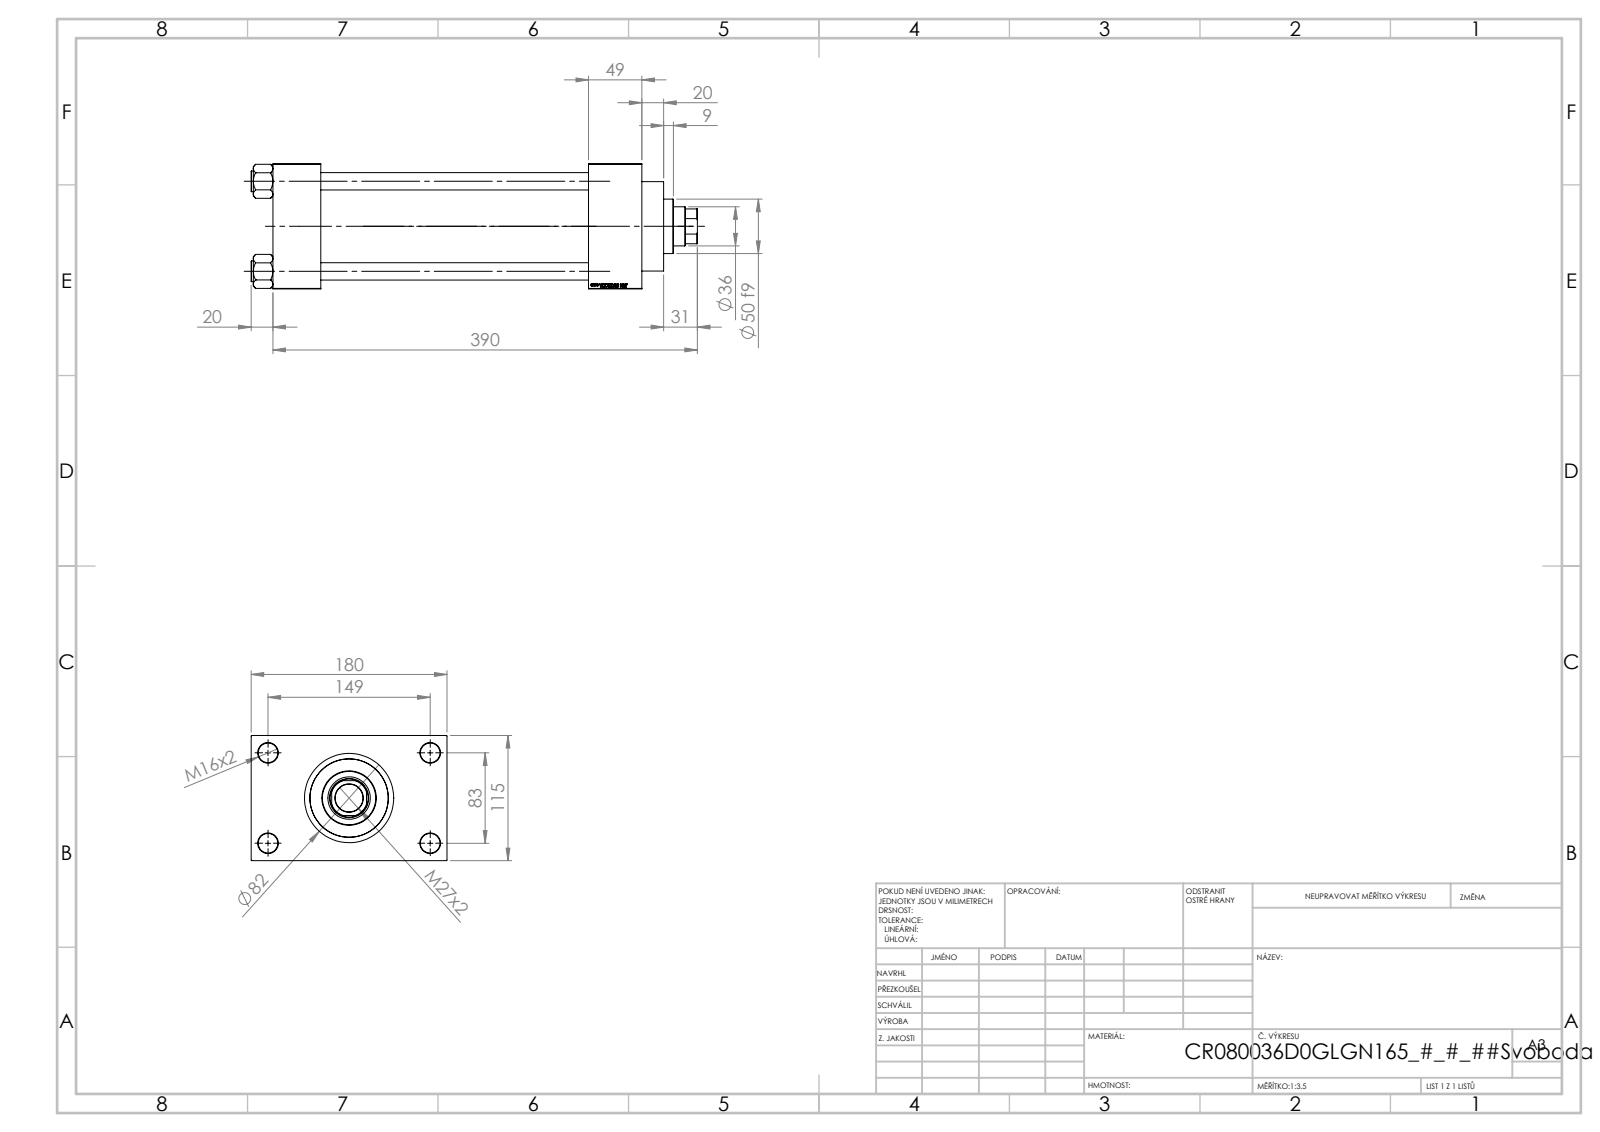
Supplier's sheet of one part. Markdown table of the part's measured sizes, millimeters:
| quantity | value |
| --- | --- |
| part name | V215CR_VCP_D; V215CR_D_Body; V215CR_D_TYCINKA; NUT_M5_D (+1 more) |
| STEP written by | SolidWorks 2019 (CONFIG_CONTROL_DESIGN) |
| units | millimeters |
| bodies | 11 solids, 1152 faces (545 planar, 89 cylindrical, 518 other) |
| overall size | 410 × 180 × 115 |
| volume | 2 466 000 mm³ |
| surface area | 444 317 mm² |
| round holes (diameter × count) | 16 × 4, 18 × 4, 7 × 2, 26.44 × 2, 35 × 2, 25.5 × 1, 36 × 1, 39 × 1, 61 × 1, 72 × 1, 80 × 1 |
| round bosses / shafts (diameter × count) | 19 × 4, 86 × 1, 82 × 1, 50 × 1 |
| partial cylindrical surfaces (radius × count) | 17.5 × 1 |
| main face-to-face distances | 115, 246, 295, 49, 44, 290, 339, 32.5, 147.5, 180 |
| hole center spacings | 33.15, 58.48, 82.7, 85.28, 89.24, 115.85, 142.43, 83 |
